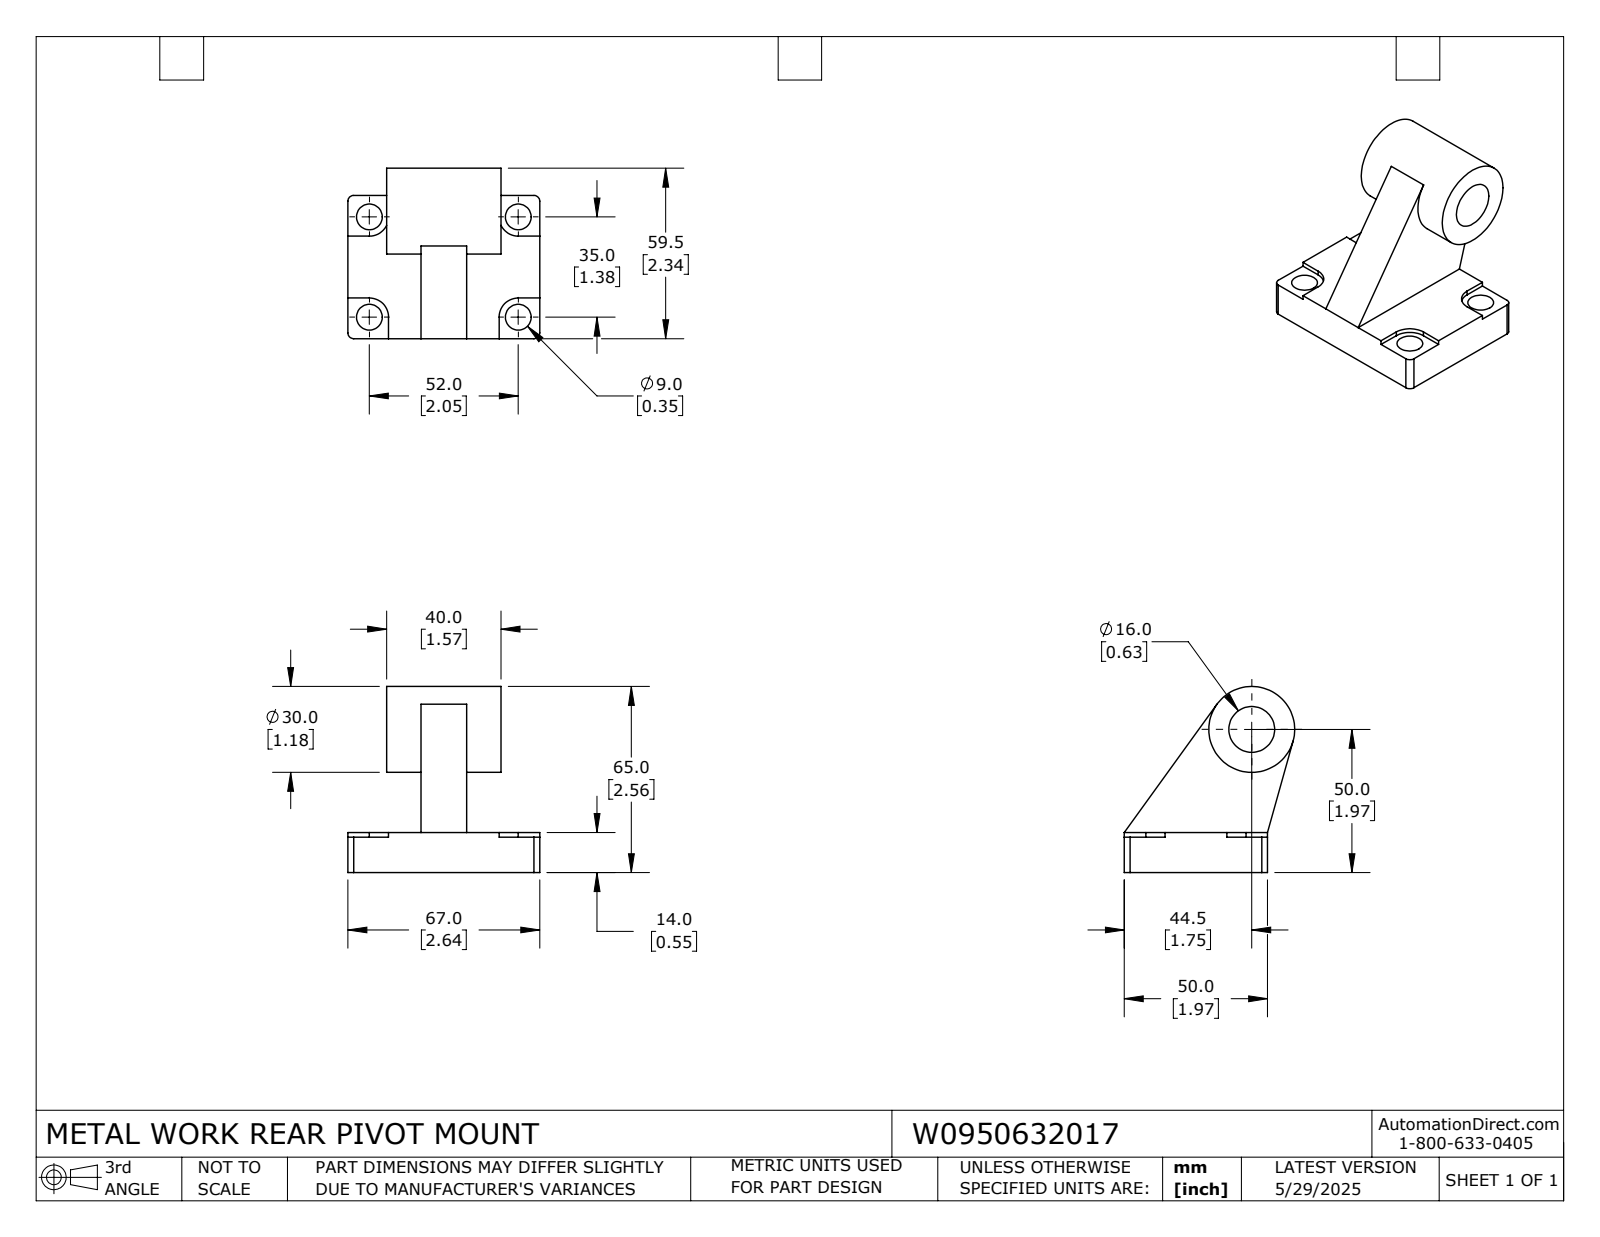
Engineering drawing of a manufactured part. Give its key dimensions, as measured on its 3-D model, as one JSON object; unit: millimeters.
{"part_name": "W0950632017", "step_written_by": "SolidWorks 2024 (CONFIG_CONTROL_DESIGN)", "units": "millimeters", "bodies": {"solids": 1, "faces": 50, "planar": 30, "cylindrical": 20, "other": 0}, "overall_size": [67, 65, 59.5], "volume_mm3": 80103, "surface_area_mm2": 19962, "round_holes": [[9, 4], [16, 1]], "round_bosses_or_shafts": [[30, 1]], "partial_cylinders_radius": [[2, 4], [6.7, 4]], "face_to_face_distances": [14, 25.5, 41.5, 16, 13.5, 53.5, 12, 28, 50, 67], "hole_center_spacings": [35, 52, 62.68]}
